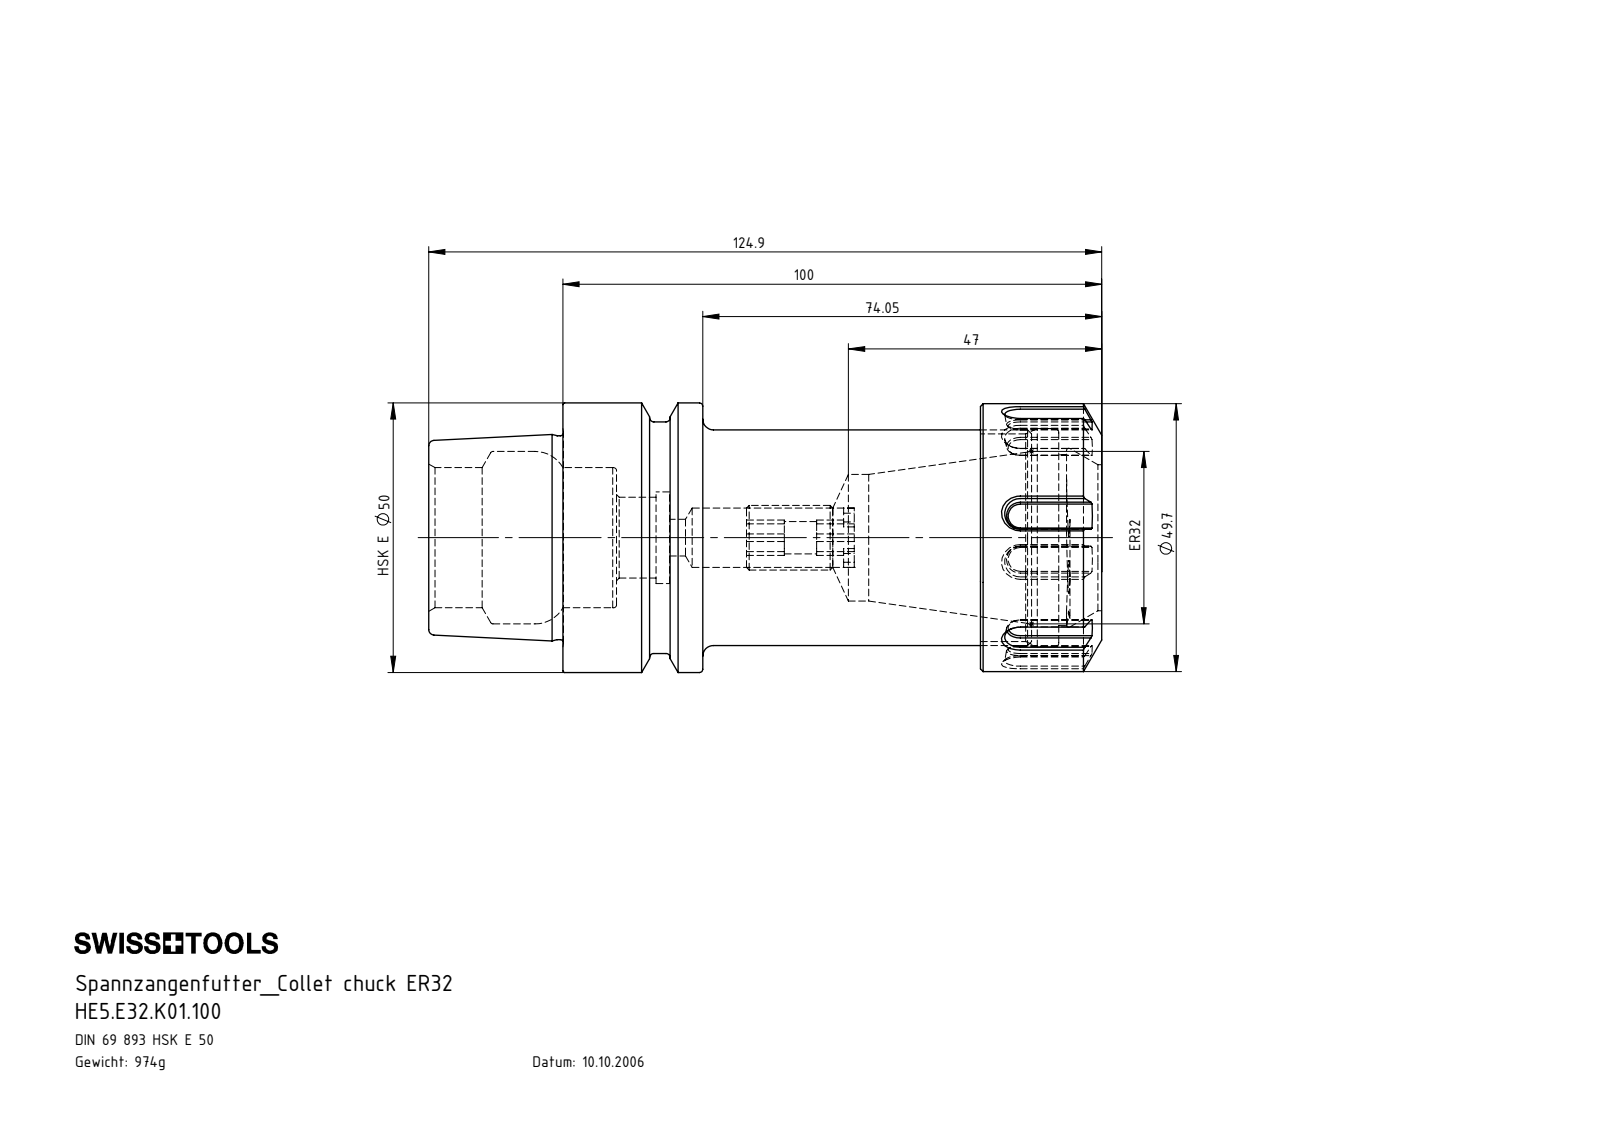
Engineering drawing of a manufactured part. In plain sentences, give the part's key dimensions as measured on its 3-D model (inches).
The part is named "E32-ER1.001.022; ERU-AN5.K01.020_A; HE5.E32.K01.100; HE5-E32.K01.100_A_Fertigbearbeitung". Its 3-D file was written by "SolidWorks 2017 (CONFIG_CONTROL_DESIGN)". It is 3 solids with 225 faces: 93 planar, 43 cylindrical and 89 other. Overall it measures 4.917 by 1.969 by 1.969 inches. Its volume is 7.57 cubic inches and its surface area 55.75 square inches. Round holes: 1 of diameter 0.236, 1 of diameter 0.268, 1 of diameter 0.433, 1 of diameter 0.591, 1 of diameter 0.669, 1 of diameter 0.925, 1 of diameter 1.024, 1 of diameter 1.067, 1 of diameter 1.26, 1 of diameter 1.516, 1 of diameter 1.594. Round bosses or shafts: 1 of diameter 1.969, 1 of diameter 1.957, 1 of diameter 1.691, 1 of diameter 1.575, 1 of diameter 1.489, 1 of diameter 0.472. Partial cylindrical surfaces (rounded edges, fillets, slot ends): 2 of radius 0.61. The main face-to-face distances are 3.051, 3.937, 0.886, 3.624, 0.573, 0.313, 1.022, 2.03, 2.602, 2.915.
